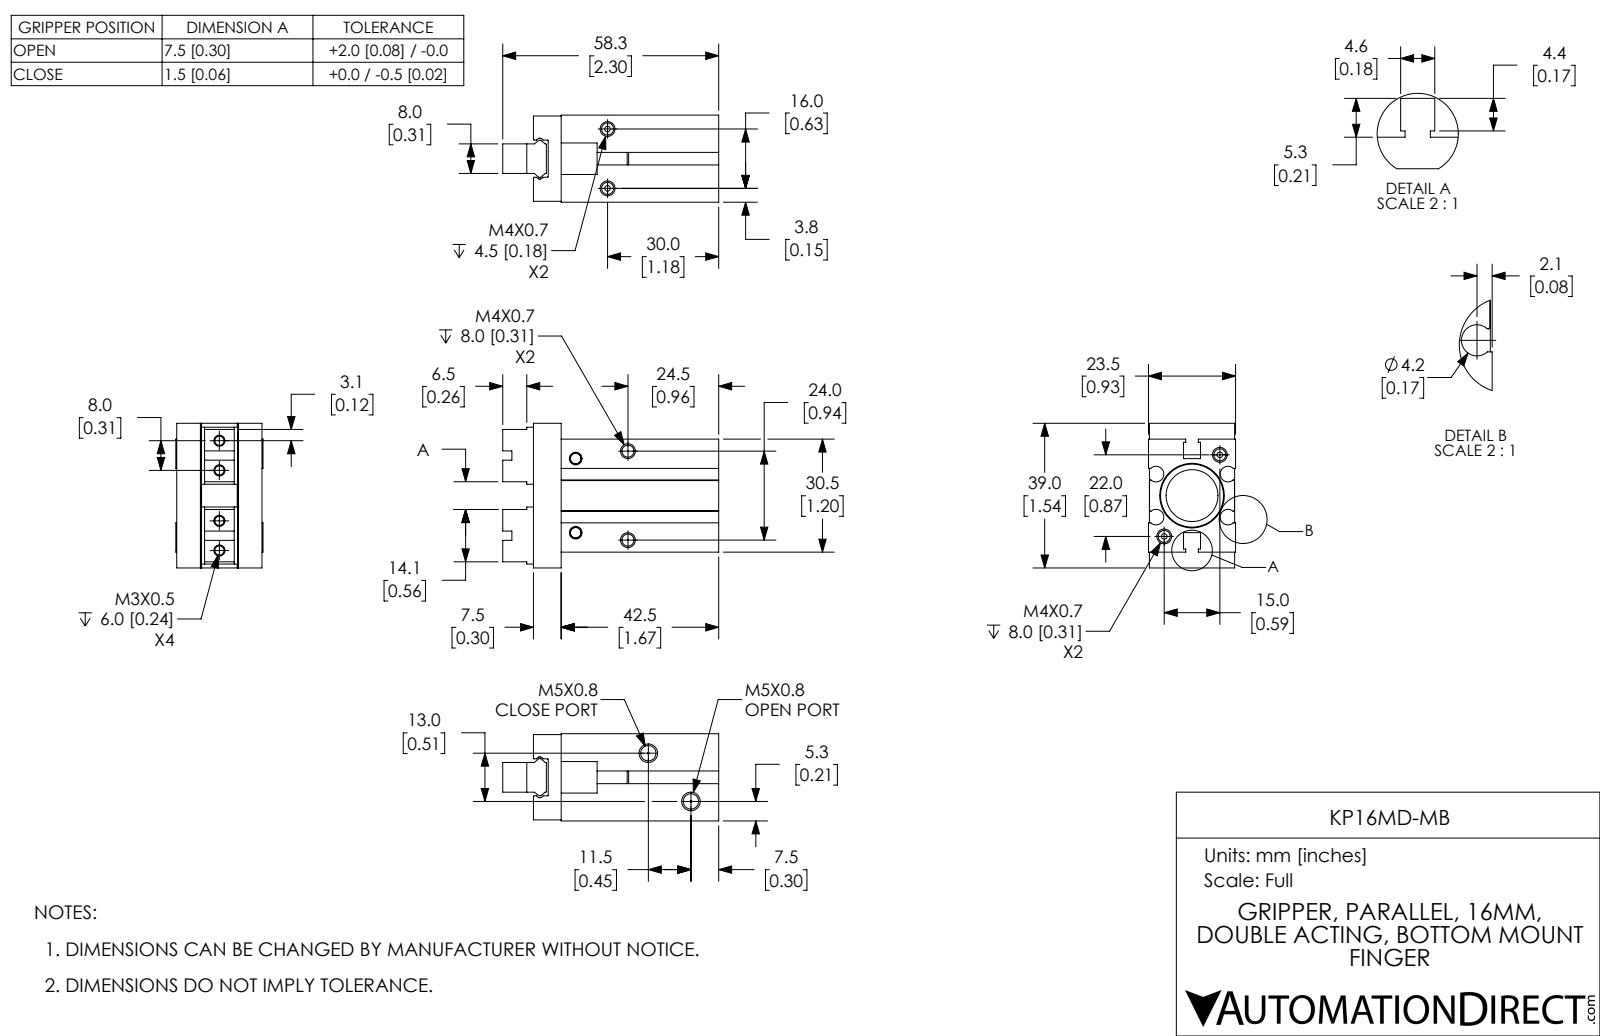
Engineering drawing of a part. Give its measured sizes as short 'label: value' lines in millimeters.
name: KP16MD-MB-1; KP16MD-MB; KP16MD-MB-3; KP16MD-MB-2
written by: SolidWorks 2017 (CONFIG_CONTROL_DESIGN)
unit: mm
bodies: 3 solids, 244 faces (124 planar, 66 cylindrical, 54 other)
size: 58.3 × 39 × 23.5
volume: 30 256 mm³; area: 13 302 mm²
holes: 6× ⌀3.24, 2× ⌀0.5, 2× ⌀2.46, 2× ⌀4.02, 2× ⌀4.13, 1× ⌀14, 1× ⌀17
rounds: 10× R0.2, 4× R2.1, 2× R0.4, 2× R0.5, 2× R1, 2× R1.23, 2× R1.23
face distances: 7.5, 15.75, 30.5, 4, 23.25, 23.2, 13.75, 23.5, 3.5, 16
hole spacings: 8.41, 13.31, 14.8, 26.87, 11.1, 16, 17.36, 18.2
